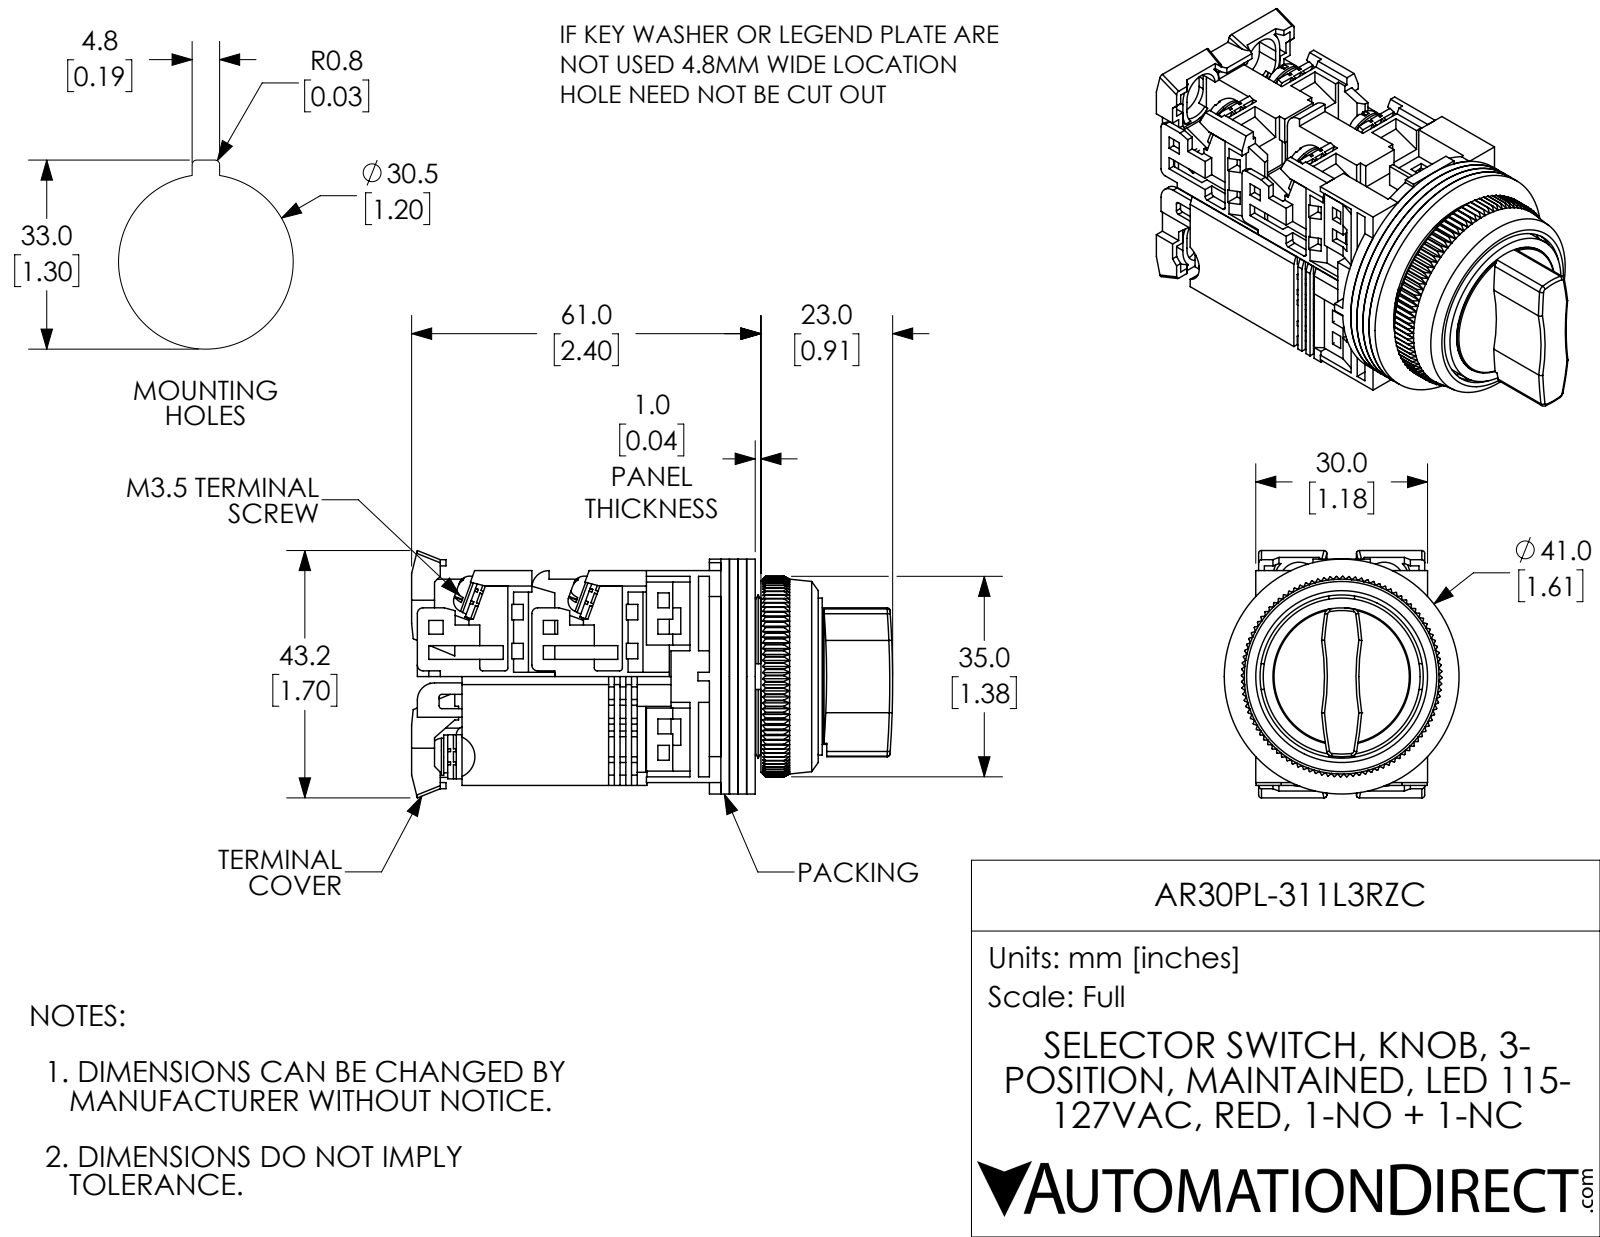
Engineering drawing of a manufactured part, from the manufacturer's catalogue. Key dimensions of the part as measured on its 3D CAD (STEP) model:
Part name (STEP PRODUCT): AR30PL-311L3RZC
STEP written by: SolidWorks 2017 (AUTOMOTIVE_DESIGN)
Units: inches
Bodies: 34 solids, 2724 faces (2033 planar, 354 cylindrical, 337 other)
Overall size (bounding box): 3.307 × 1.7 × 1.614
Volume: 3.442 in³ · Surface area: 70.72 in²
Round holes (diameter × count): ⌀0.138 ×8, ⌀0.142 ×6, ⌀0.118 ×3, ⌀0.472 ×1, ⌀0.709 ×1, ⌀0.768 ×1, ⌀0.827 ×1, ⌀1.122 ×1, ⌀1.181 ×1, ⌀1.252 ×1
Round bosses / shafts (diameter × count): ⌀0.26 ×6, ⌀0.138 ×4, ⌀0.063 ×2, ⌀1.614 ×1, ⌀1.15 ×1, ⌀1.079 ×1, ⌀0.945 ×1, ⌀0.886 ×1
Partial cylindrical surfaces — rounded edges, fillets, slot ends (radius × count): R0.059 ×25, R0.02 ×15, R0.039 ×8, R0.138 ×4, R0.177 ×4, R0.118 ×3, R1.575 ×2, R2.953 ×2
Main face-to-face distances: 0.059, 0.118, 0.177, 0.039, 0.748, 0.079, 0.787, 0.063, 0.689, 0.197
Hole centre spacings: 0.579, 0.269, 0.638, 0.297, 0.624, 0.02, 0.302, 0.583
